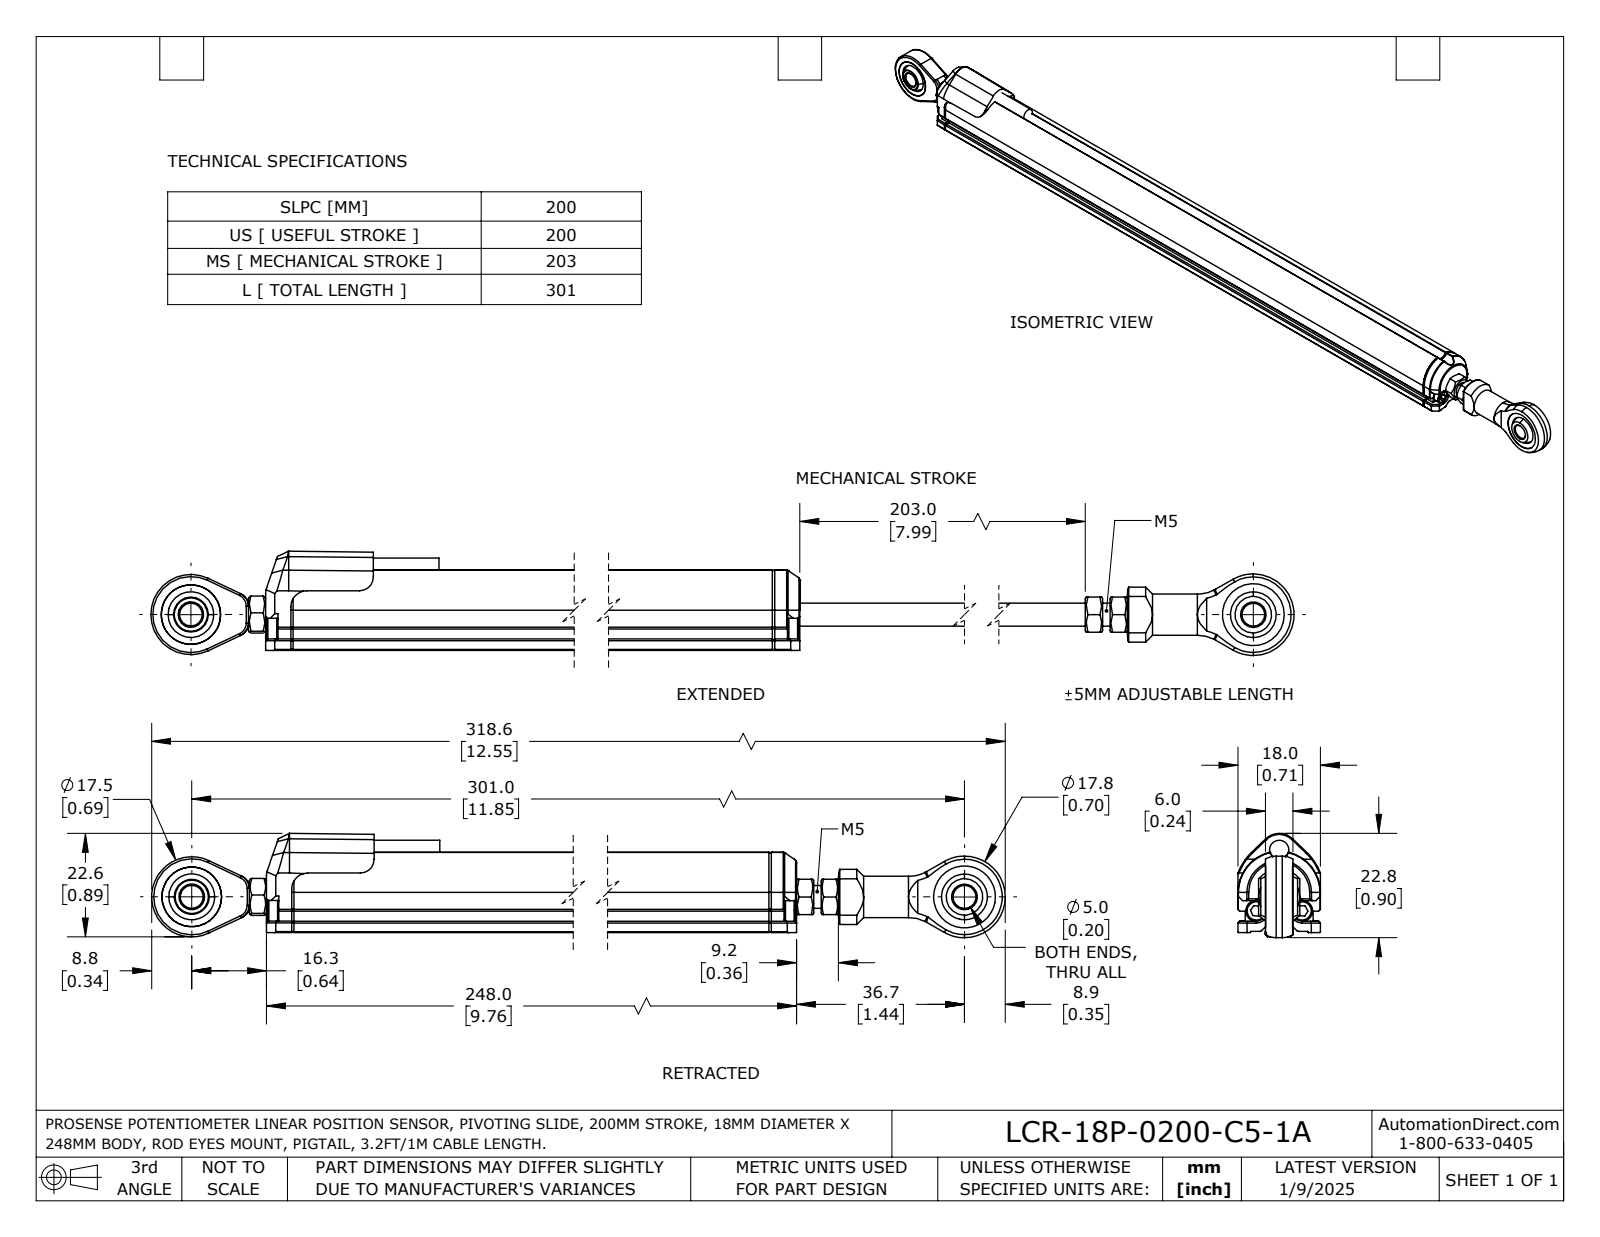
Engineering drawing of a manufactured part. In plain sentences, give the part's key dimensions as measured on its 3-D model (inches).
The part is named "LCR-18P-0200-C5-1A". Its 3-D file was written by "SolidWorks 2023 (AUTOMOTIVE_DESIGN)". It is 20 solids with 515 faces: 289 planar, 136 cylindrical and 90 other. Overall it measures 12.545 by 0.896 by 0.709 inches. Its volume is 4.348 cubic inches and its surface area 45.29 square inches. Round holes: 4 of diameter 0.197, 2 of diameter 0.102, 2 of diameter 0.104, 2 of diameter 0.394, 1 of diameter 0.213, 1 of diameter 0.272, 1 of diameter 0.512, 1 of diameter 0.531. Round bosses or shafts: 4 of diameter 0.181, 3 of diameter 0.113, 2 of diameter 0.059, 1 of diameter 0.354, 1 of diameter 0.165, 1 of diameter 0.113. Partial cylindrical surfaces (rounded edges, fillets, slot ends): 12 of radius 0.008, 10 of radius 0.004, 8 of radius 0.02, 6 of radius 0.012, 6 of radius 0.018, 4 of radius 0.016, 4 of radius 0.039, 4 of radius 0.043. The main face-to-face distances are 0.709, 0.059, 0.063, 0.646, 0.071, 0.02, 9.311, 0.236, 0.087, 0.098. The hole center spacings are 0.231, 0.394, 0.23, 0.231, 11.85.
